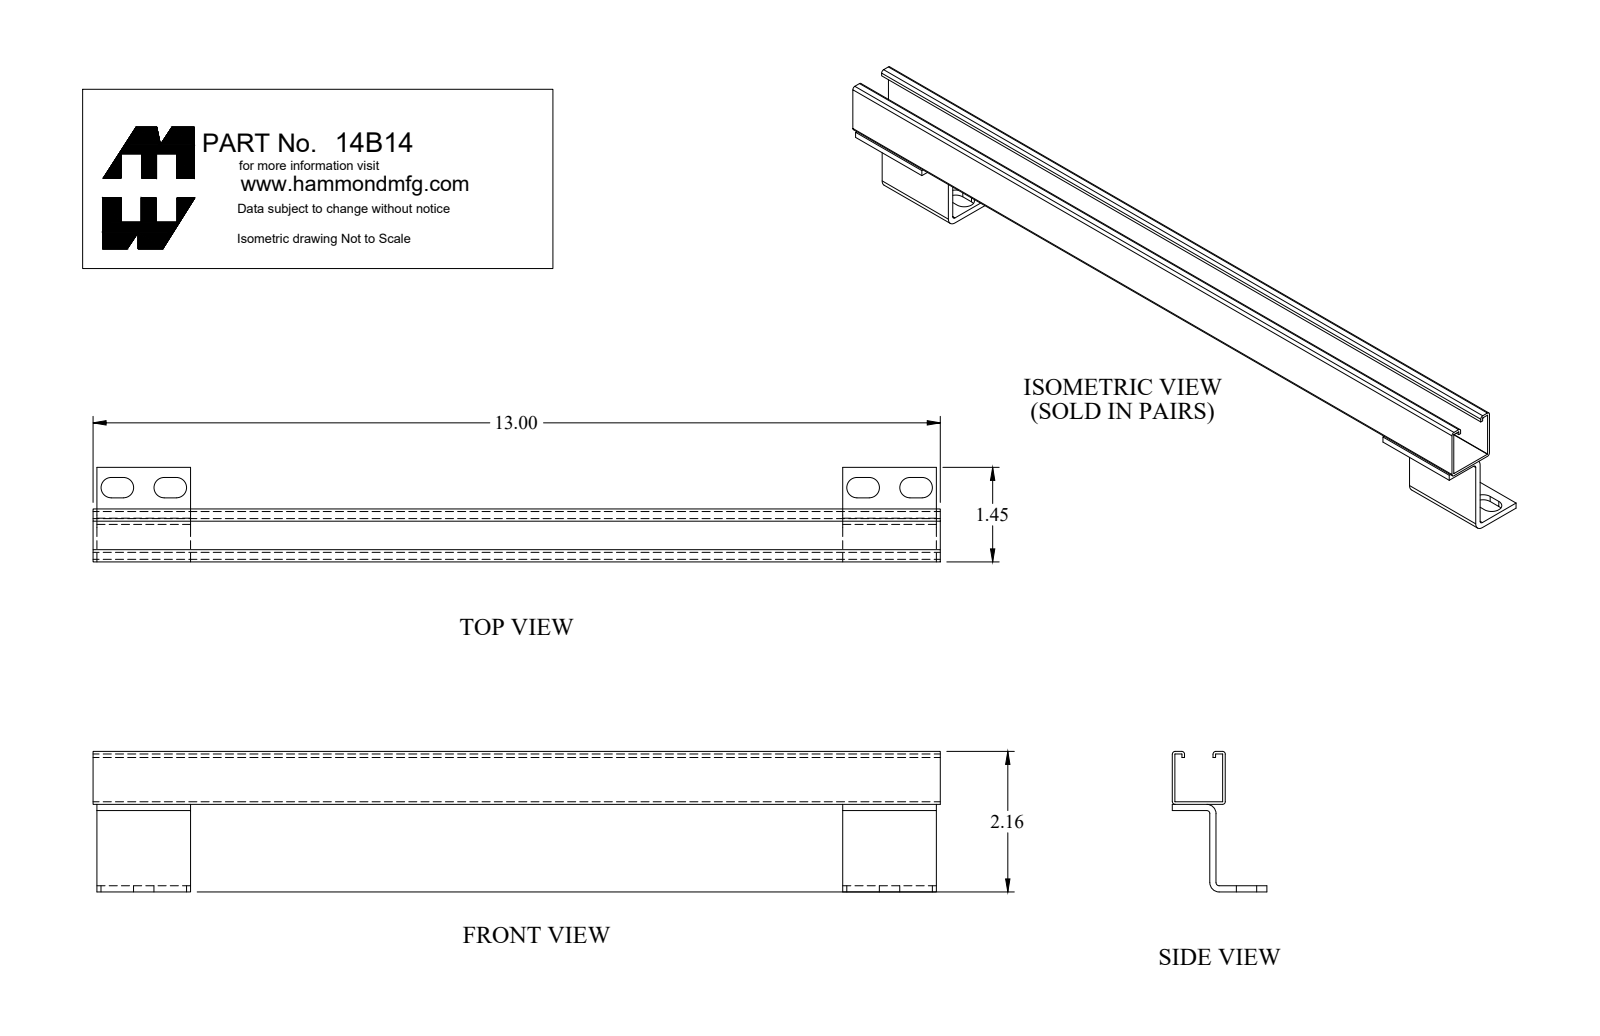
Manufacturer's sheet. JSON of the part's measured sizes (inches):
{"part_name": "14B14", "step_written_by": "SolidWorks 2018 (AUTOMOTIVE_DESIGN)", "units": "inches", "bodies": {"solids": 3, "faces": 74, "planar": 46, "cylindrical": 28, "other": 0}, "overall_size": [13, 2.156, 1.451], "volume_in3": 2.069, "surface_area_in2": 87.57, "partial_cylinders_radius": [[0.156, 8], [0.043, 6], [0.048, 2], [0.143, 2]], "face_to_face_distances": [0.04, 0.773, 0.813, 0.733, 0.095, 0.773, 1.248, 0.142, 0.237, 0.102]}
